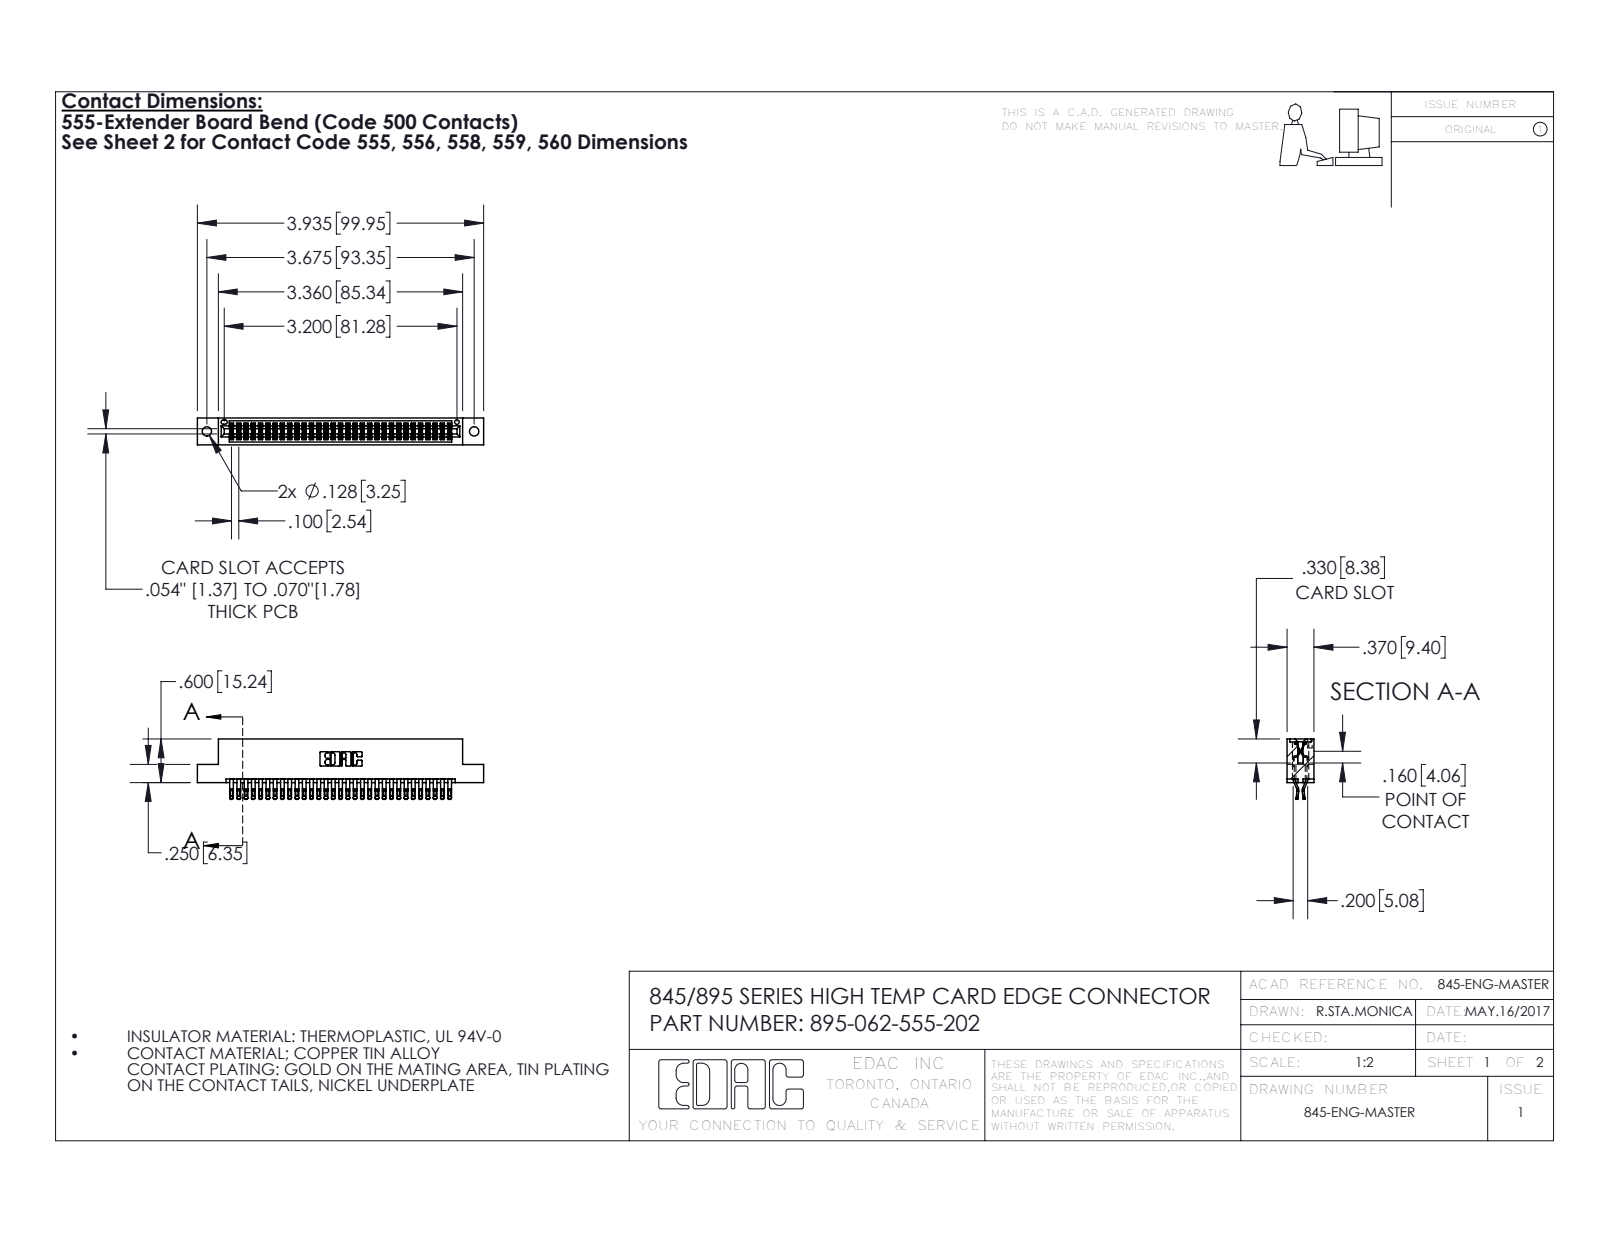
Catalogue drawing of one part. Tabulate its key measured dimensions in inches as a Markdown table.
| quantity | value |
| --- | --- |
| part name | 345-292-001_555 Tail; 395-062-555-202; 345 Part_Flush Mounting Lugs - 0.128 Dia |
| STEP written by | SolidWorks 2016 (CONFIG_CONTROL_DESIGN) |
| units | inches |
| bodies | 63 solids, 3598 faces (2002 planar, 1596 cylindrical, 0 other) |
| overall size | 3.935 × 0.832 × 0.37 |
| volume | 0.595 in³ |
| surface area | 22.56 in² |
| round holes (diameter × count) | 0.128 × 2, 0.064 × 1 |
| partial cylindrical surfaces (radius × count) | 0.016 × 155, 0.02 × 124, 0.006 × 93, 0.01 × 22, 0.007 × 6, 0.031 × 6, 0.026 × 3, 0.01 × 2 |
| main face-to-face distances | 0.298, 0.072, 0.2, 0.37, 0.025, 0.098, 0.272, 0.225, 0.175, 0.149 |
| hole center spacings | 0.27, 3.44, 3.675 |
